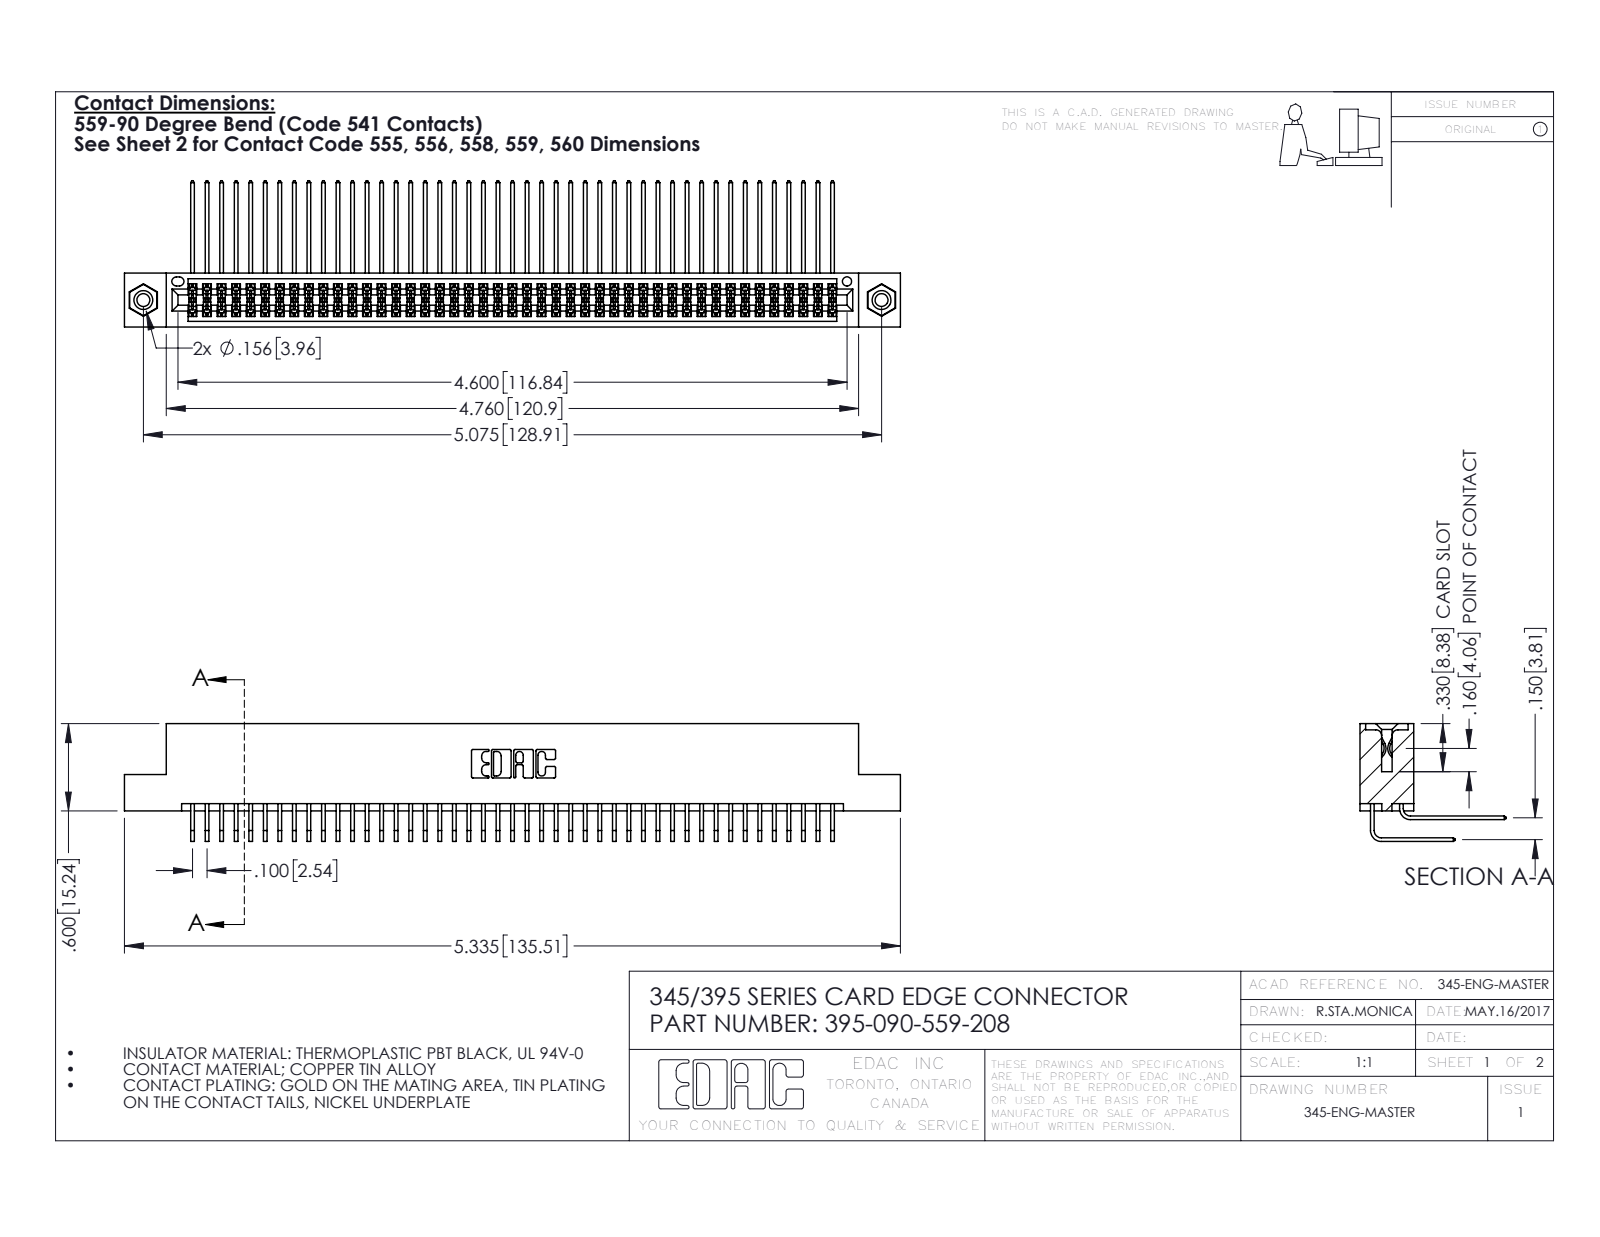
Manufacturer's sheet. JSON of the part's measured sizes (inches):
{"part_name": "345-292-001_558 559 Tail - 1; 345-250-001_345-250-003-102; 345-292-001_559 Tail - 2; 345 Part_Flush Mounting Lugs - 0.156 Dia-TI (+1 more)", "step_written_by": "SolidWorks 2016 (CONFIG_CONTROL_DESIGN)", "units": "inches", "bodies": {"solids": 93, "faces": 4866, "planar": 3262, "cylindrical": 1588, "other": 16}, "overall_size": [5.335, 1.005, 0.809], "volume_in3": 0.836, "surface_area_in2": 35.29, "round_holes": [[0.089, 2], [0.125, 2], [0.156, 2], [0.064, 1]], "round_bosses_or_shafts": [[0.155, 2]], "partial_cylinders_radius": [[0.006, 136], [0.01, 22], [0.007, 6], [0.031, 6], [0.026, 3], [0.014, 2], [0.019, 2], [0.022, 2]], "face_to_face_distances": [0.072, 0.298, 0.2, 0.37, 0.098, 0.272, 0.025, 0.225, 0.175, 0.15], "hole_center_spacings": [0.27, 4.839, 5.075]}
